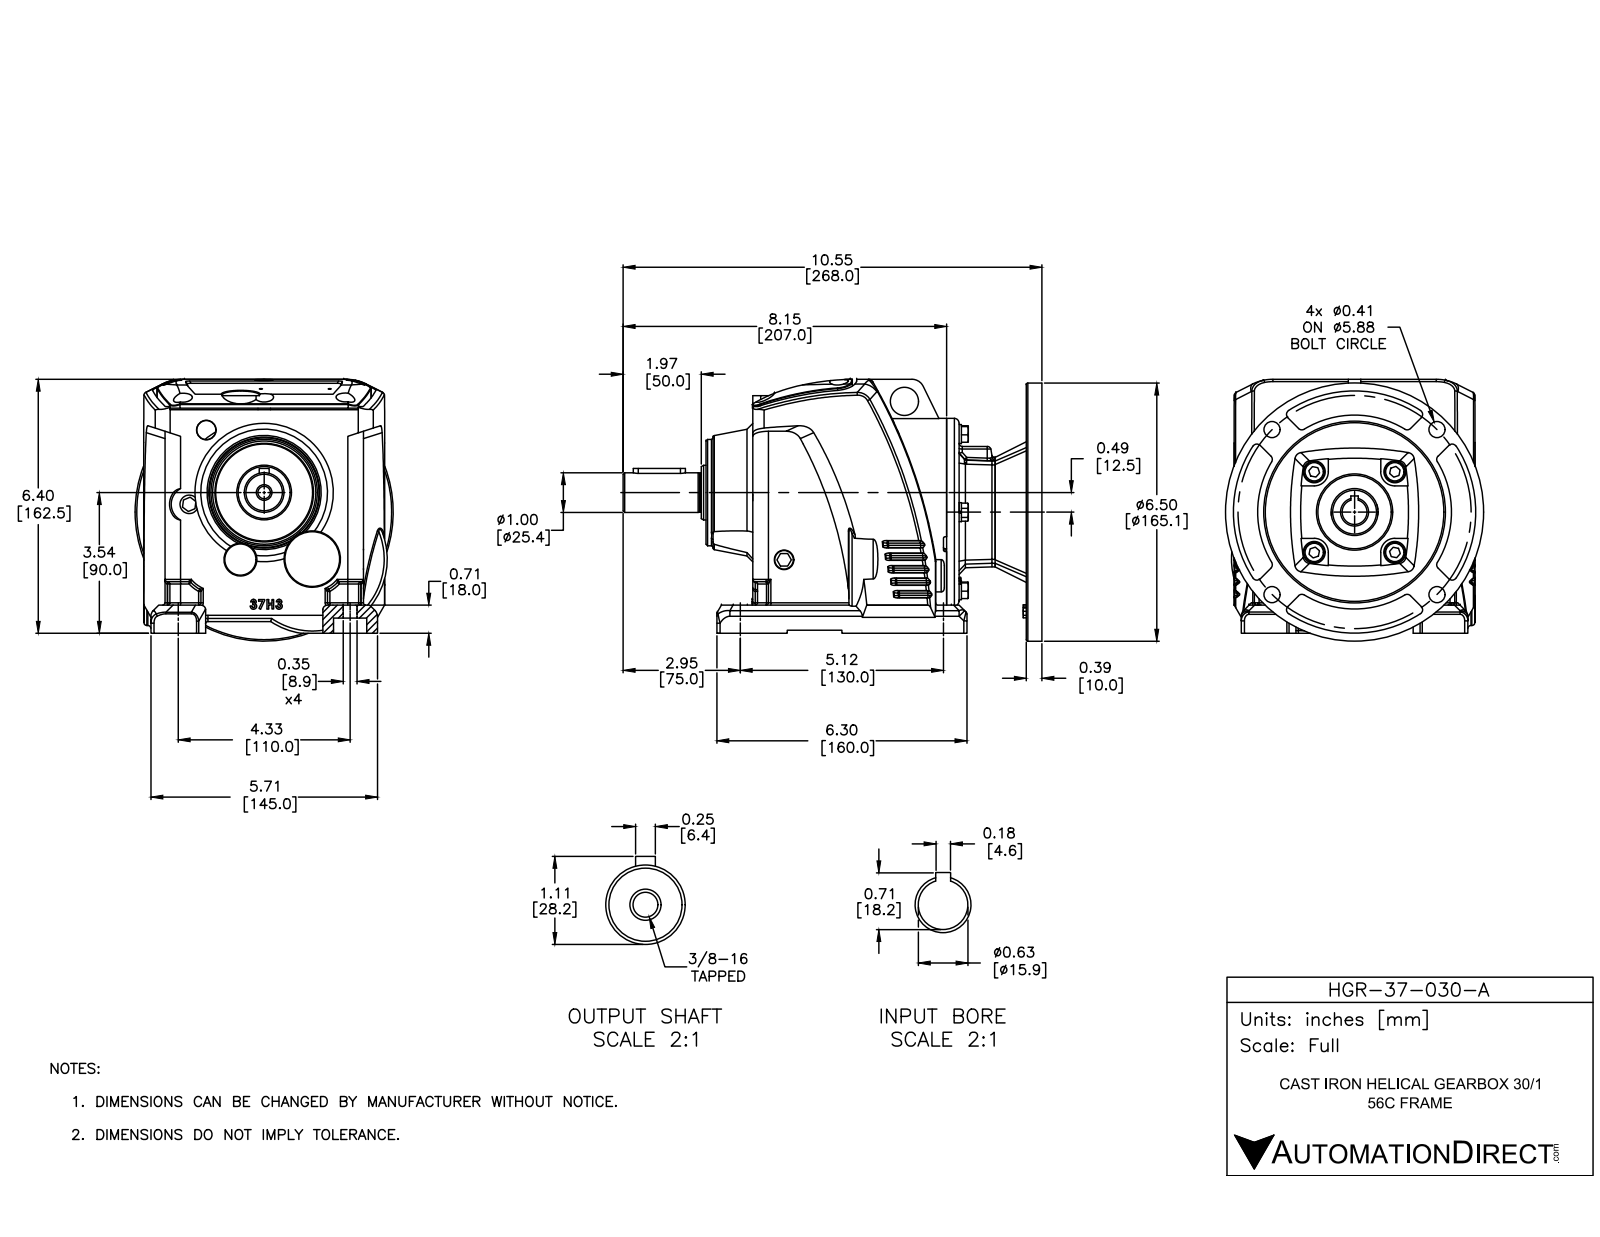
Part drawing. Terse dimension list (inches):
name: HGR-37-030-A
written by: SolidWorks 2015 (AUTOMOTIVE_DESIGN)
unit: in
bodies: 4 solids, 1036 faces (343 planar, 277 cylindrical, 416 other)
size: 10.551 × 6.596 × 6.5
volume: 169.7 in³; area: 383.8 in²
holes: 6× ⌀0.472, 4× ⌀0.406, 4× ⌀0.55, 3× ⌀0.276, 2× ⌀0.079, 2× ⌀0.354, 2× ⌀0.394, 1× ⌀0.313, 1× ⌀0.625, 1× ⌀0.709, 1× ⌀0.945, 1× ⌀1.181
bosses: 4× ⌀0.512, 4× ⌀0.48, 4× ⌀0.315, 2× ⌀1.378, 2× ⌀0.472, 1× ⌀6.5, 1× ⌀4.724, 1× ⌀2.677
rounds: 43× R0.059, 21× R0.118, 18× R0.079, 8× R0.197, 6× R0.354, 6× R0.394, 5× R0.315, 4× R0.276
face distances: 7.126, 0.236, 0.276, 0.394, 6.89, 1.102, 4.331, 0.157, 2.087, 0.079
hole spacings: 3.27, 1.437, 1.5, 2.032, 2.937, 4.154, 4.374, 1.143
